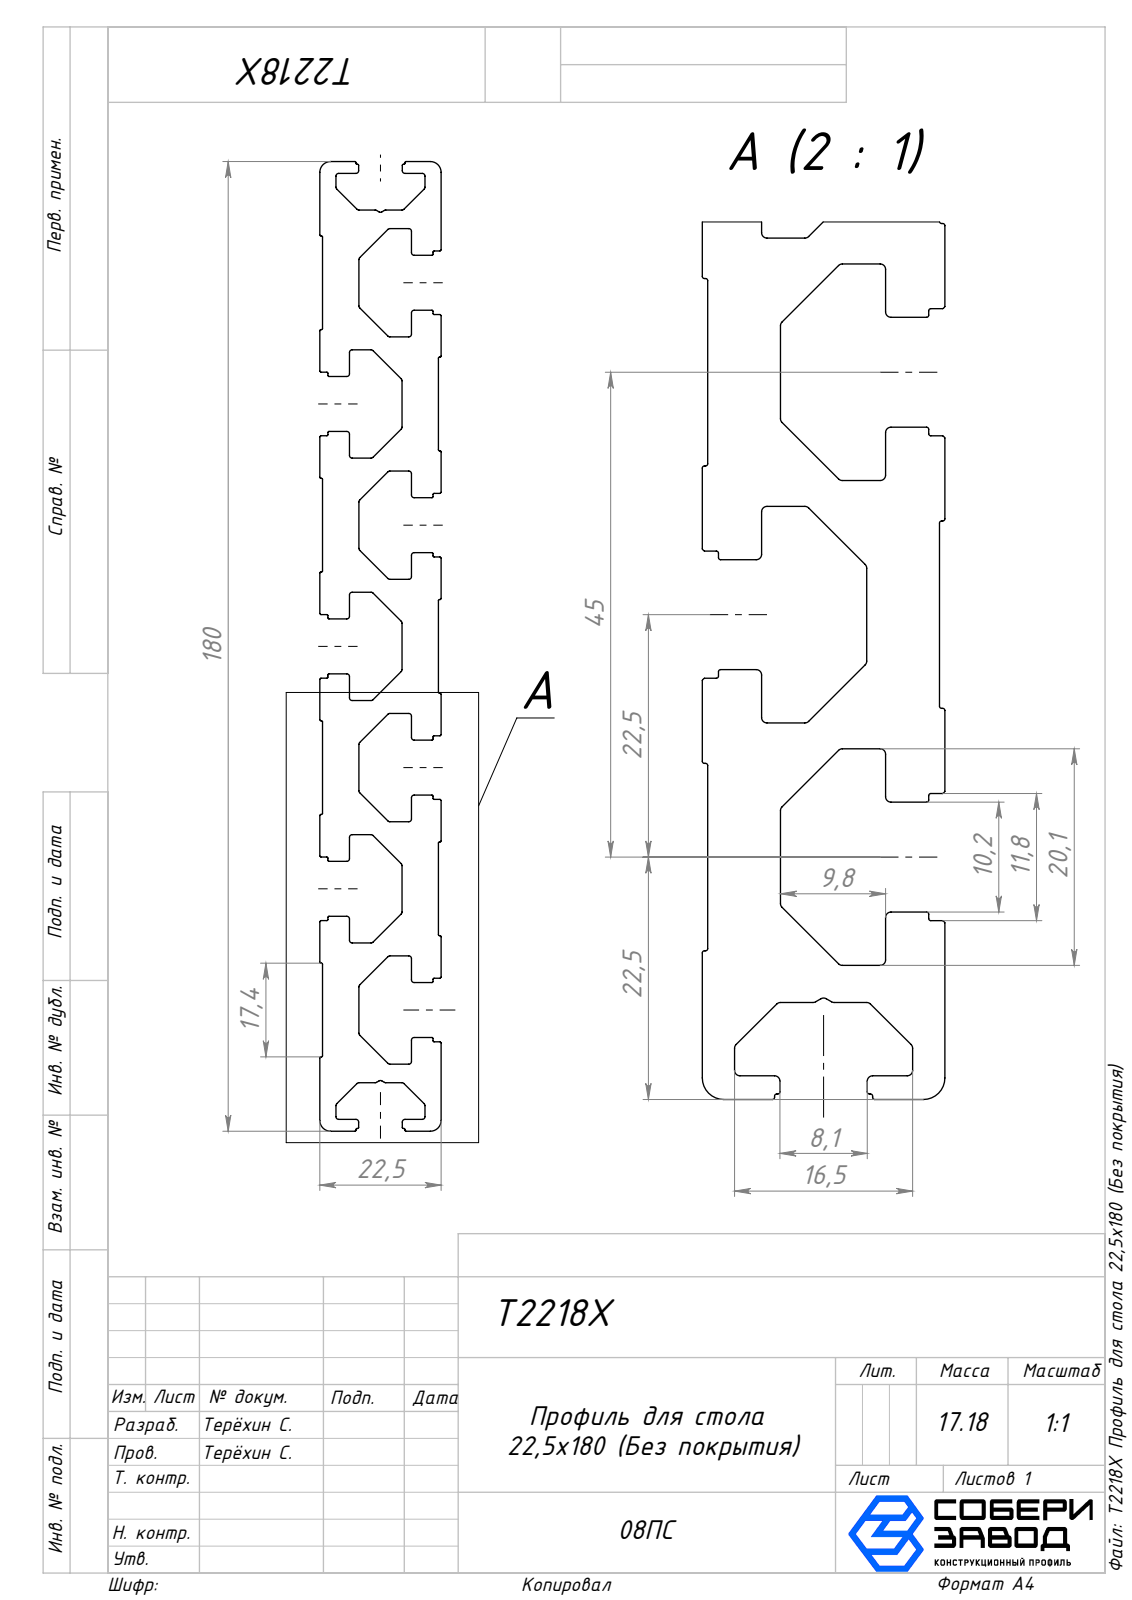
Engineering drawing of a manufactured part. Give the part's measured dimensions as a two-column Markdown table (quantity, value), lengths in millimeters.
| quantity | value |
| --- | --- |
| part name | T2218X Профиль для стола 22,5х180 (Без покрытия); T2218X Профиль для стола 22,5х180 (Без покрытия)_00 |
| STEP written by | SolidWorks 2025 (CONFIG_CONTROL_DESIGN) |
| units | millimeters |
| bodies | 1 solid, 331 faces (166 planar, 165 cylindrical, 0 other) |
| overall size | 1000 × 180 × 22.5 |
| volume | 2 189 000 mm³ |
| surface area | 764 313 mm² |
| partial cylindrical surfaces (radius × count) | 0.5 × 78, 0.2 × 68, 0.56 × 14, 2 × 4 |
| main face-to-face distances | 0.5, 22, 22.5, 7.25, 15.25, 6.75, 14.75, 5.5, 17, 5 |
